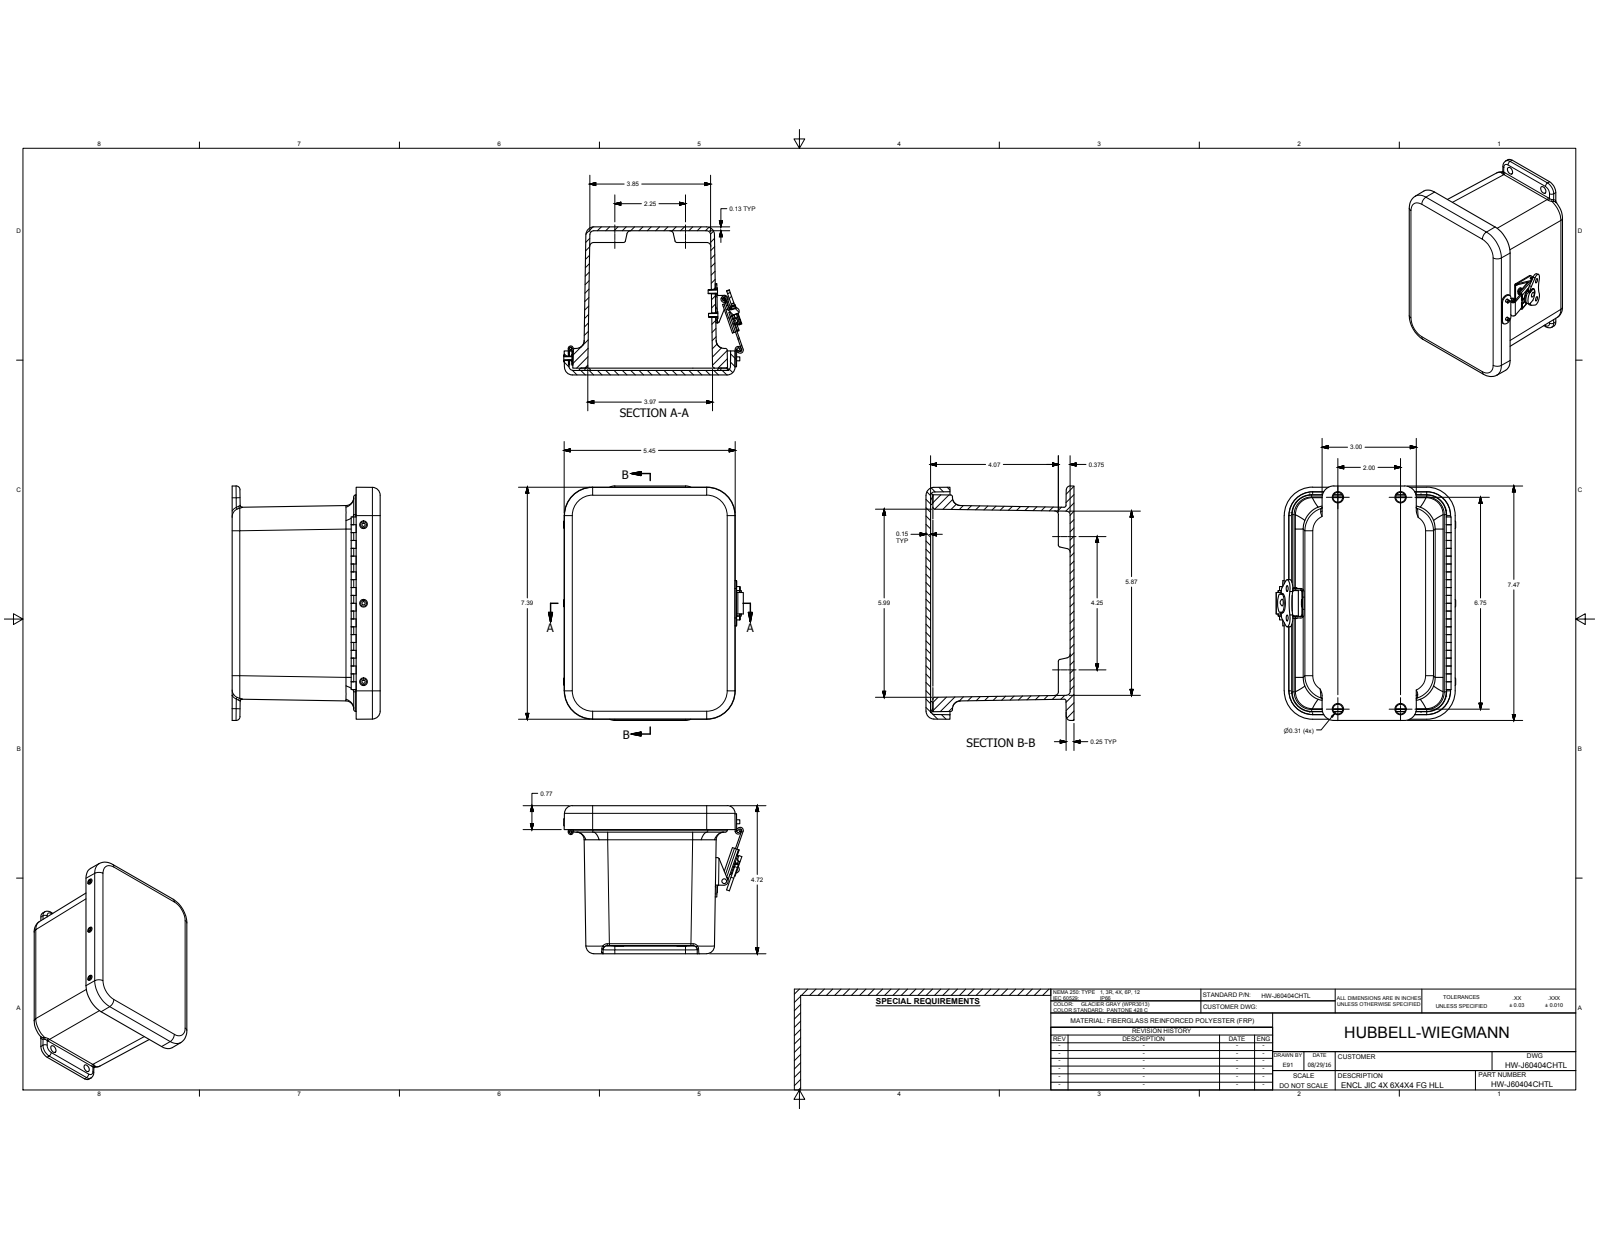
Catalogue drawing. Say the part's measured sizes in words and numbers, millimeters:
The part is named "HW-J604CHTL; WP604H&LBOX; WP604HLU; WP604HCVR (+8 more)". Its 3-D file was written by "Autodesk Inventor 2017 (CONFIG_CONTROL_DESIGN)". It is 29 solids with 787 faces: 290 planar, 317 cylindrical and 180 other. Overall it measures 189.74 by 145.65 by 119.83 millimeters. Its volume is 481 795 cubic millimeters and its surface area 261 525 square millimeters. Round holes: 10 of diameter 3.56, 9 of diameter 2.64, 8 of diameter 3.86, 5 of diameter 3.33, 4 of diameter 4.04, 4 of diameter 5.54, 2 of diameter 3.3, 2 of diameter 3.38, 2 of diameter 4.75, 1 of diameter 1.7, 1 of diameter 2.16, 1 of diameter 2.49. Round bosses or shafts: 9 of diameter 3.17, 4 of diameter 6.86, 1 of diameter 16.76, 1 of diameter 14.78, 1 of diameter 13.34, 1 of diameter 7.26, 1 of diameter 5.41, 1 of diameter 4.57. Partial cylindrical surfaces (rounded edges, fillets, slot ends): 43 of radius 3.17, 18 of radius 1.59, 11 of radius 6.35, 8 of radius 0.38, 8 of radius 1.88, 8 of radius 15.88, 7 of radius 1.52, 4 of radius 0.29. The main face-to-face distances are 3.68, 116.15, 119.83, 3.18, 112.97, 116.65, 111.12, 114.3, 8.85, 1.85. The hole center spacings are 63.5, 101.6, 127, 57.15, 84.82, 122.15, 154.99, 7.13.
